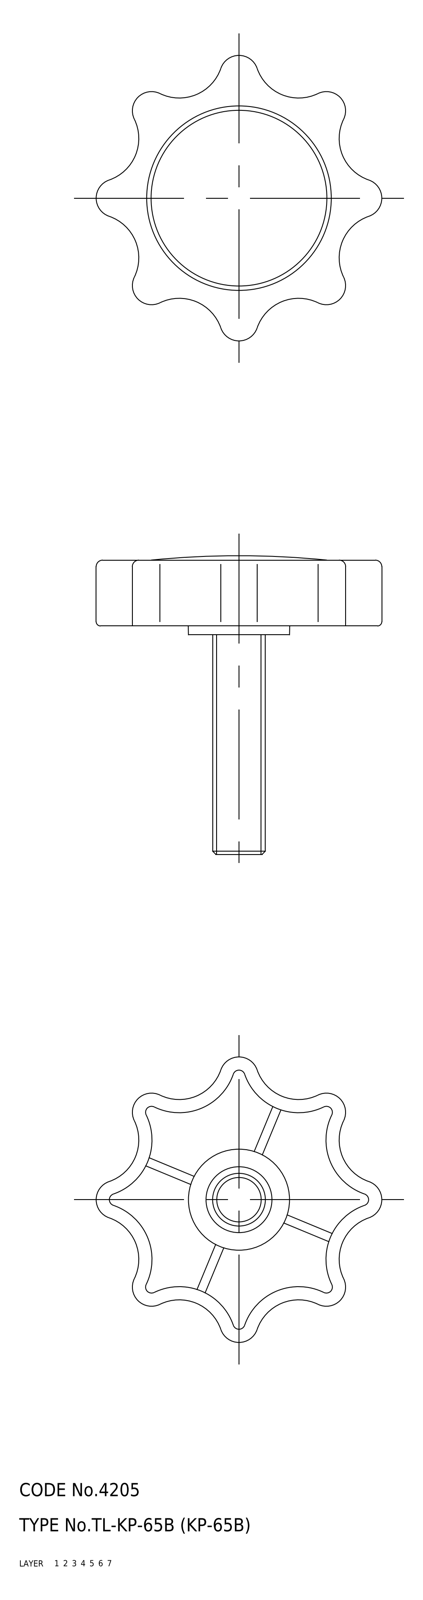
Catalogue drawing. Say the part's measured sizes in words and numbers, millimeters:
The part is named "screw; knob; KP_65B_8212_36". Its 3-D file was written by "CADfix (AUTOMOTIVE_DESIGN)". It is 2 solids with 120 faces: 0 planar, 0 cylindrical and 120 other. Overall it measures 68 by 65 by 65 millimeters. Its volume is 29 476 cubic millimeters and its surface area 15 500 square millimeters.
